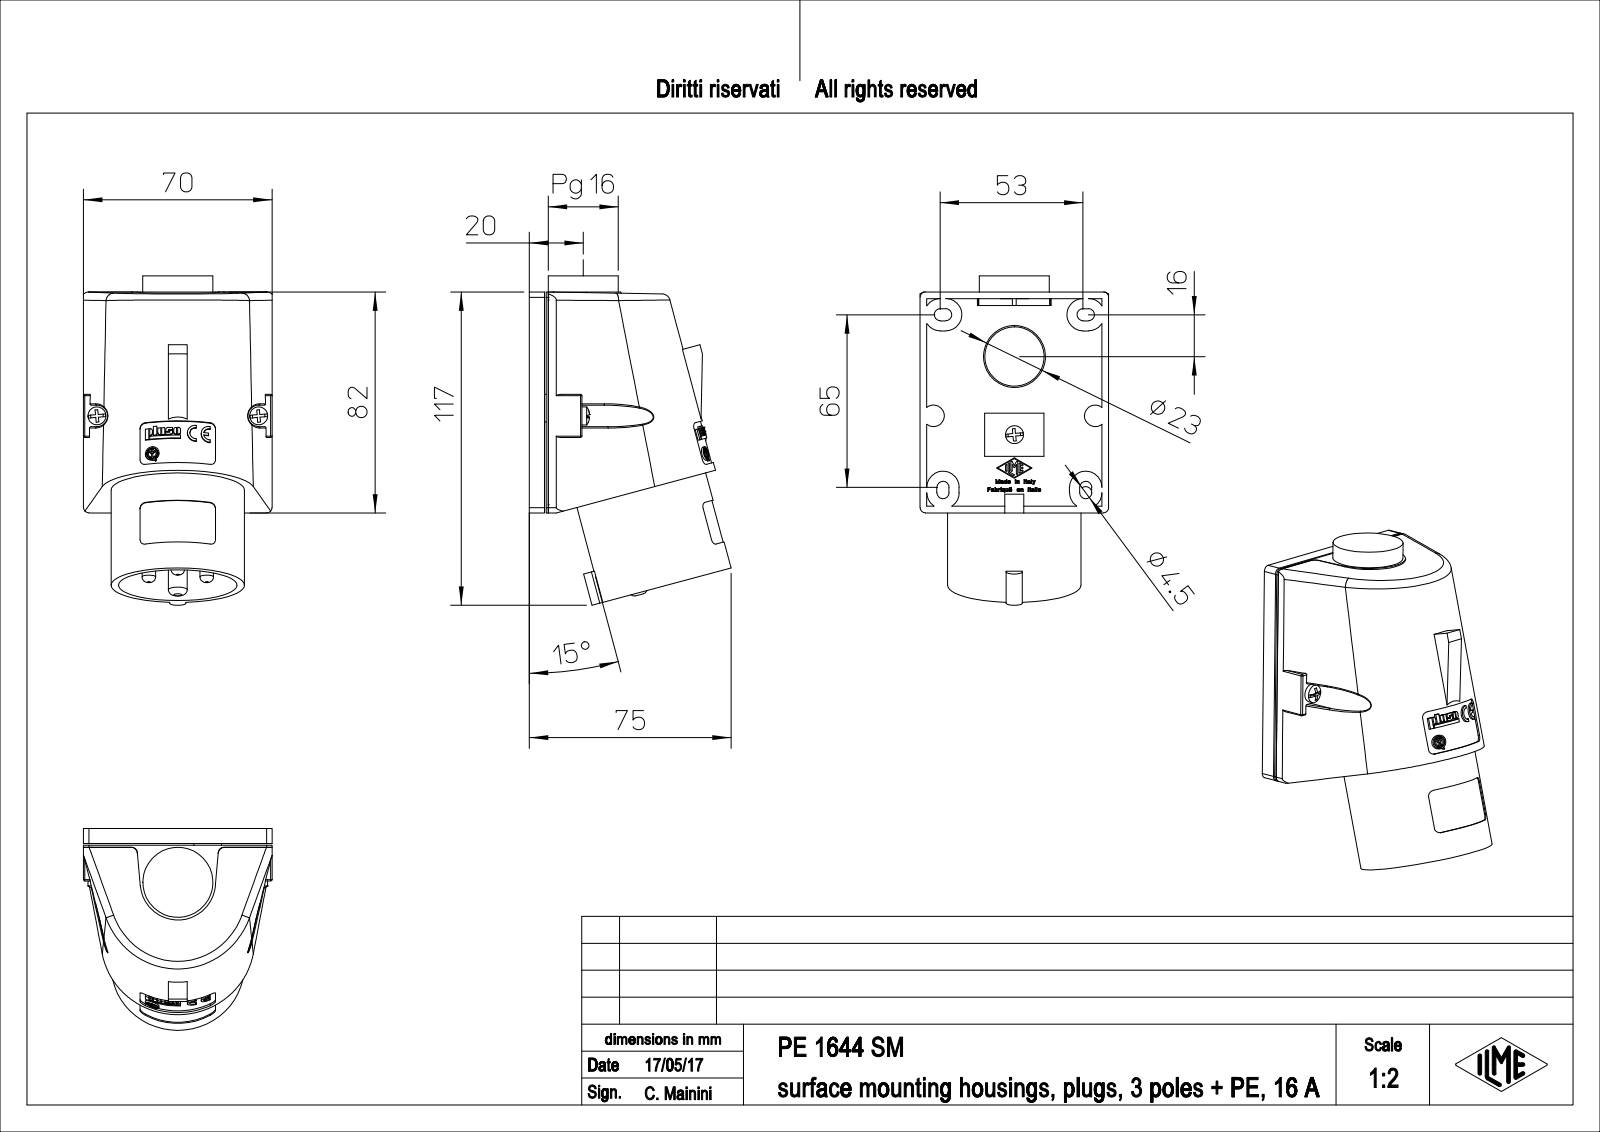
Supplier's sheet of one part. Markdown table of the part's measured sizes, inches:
| quantity | value |
| --- | --- |
| part name | PE_1644_SM |
| STEP written by | PTC Creo Elements/Direct Modeling 19.0E 27-Jun-2016 (C) Parametric Technology GmbH (AUTOMOTIVE_DESIGN) |
| units | inches |
| bodies | 1 solid, 2014 faces (1701 planar, 233 cylindrical, 80 other) |
| overall size | 4.813 × 2.949 × 2.756 |
| volume | 15.27 in³ |
| surface area | 97.73 in² |
| round holes (diameter × count) | 0.236 × 4, 0.126 × 2, 0.165 × 2, 0.169 × 2, 0.177 × 2, 0.118 × 1, 0.839 × 1, 0.906 × 1, 1.732 × 1 |
| round bosses / shafts (diameter × count) | 0.197 × 6, 0.264 × 5, 1.024 × 2, 1.949 × 1, 1.654 × 1, 0.403 × 1, 0.276 × 1 |
| partial cylindrical surfaces (radius × count) | 0.02 × 17, 0.01 × 15, 0.079 × 15, 0.236 × 12, 0.034 × 9, 0.089 × 8, 0.157 × 8, 0.039 × 6 |
| main face-to-face distances | 0.098, 0.237, 0.139, 0.138, 0.108, 0.031, 0.206, 0.025, 0.083, 0.056 |
| hole center spacings | 0.423, 0.598, 0.599, 0.846, 1.213, 1.465, 0.424, 1.142 |
